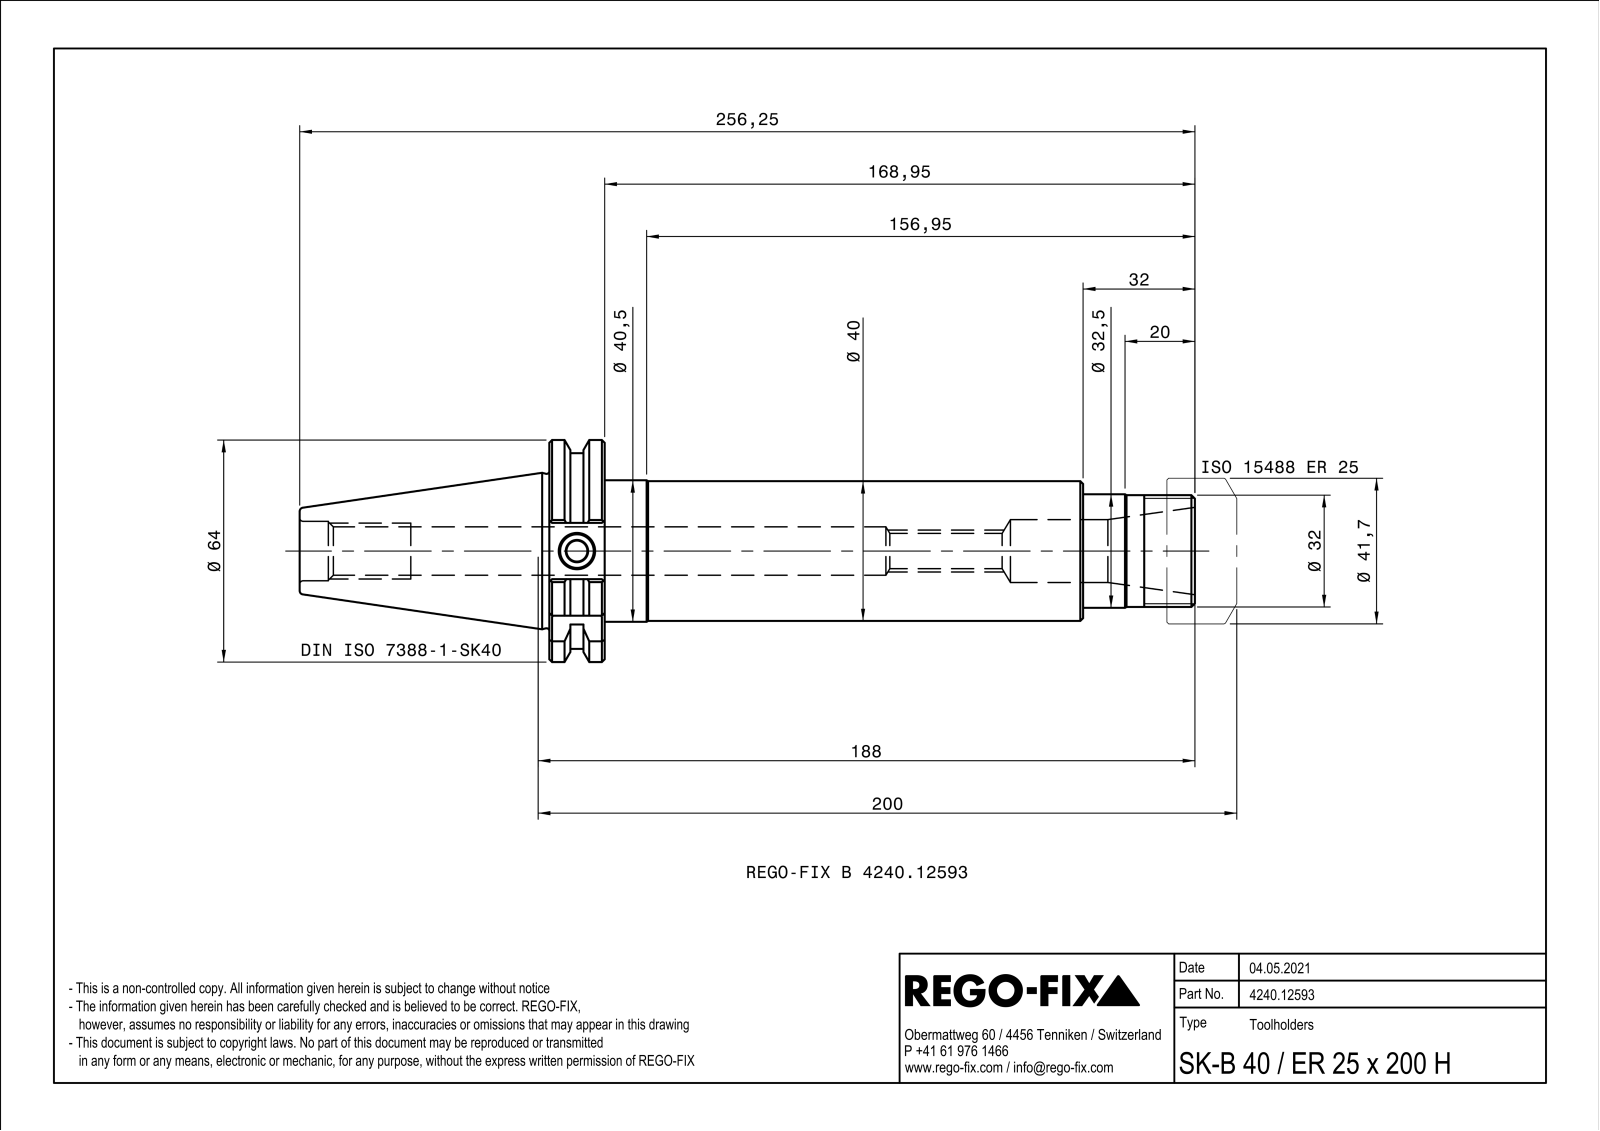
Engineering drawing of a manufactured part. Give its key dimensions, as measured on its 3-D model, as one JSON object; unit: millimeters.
{"part_name": "NOCUT", "step_written_by": "SIEMENS PLM Software Solid Edge ST10 (AUTOMOTIVE_DESIGN)", "units": "millimeters", "bodies": {"solids": 1, "faces": 160, "planar": 45, "cylindrical": 52, "other": 63}, "overall_size": [256.25, 63.55, 61.01], "volume_mm3": 265080, "surface_area_mm2": 49106, "round_holes": [[3.9, 2], [3.24, 1], [6, 1], [10, 1], [10.11, 1], [13.83, 1], [13.84, 1], [17, 1], [18, 1]], "round_bosses_or_shafts": [[40.5, 1], [40, 1], [32.5, 1], [32, 1]], "partial_cylinders_radius": [[0.5, 13], [2.25, 2], [28, 1], [31.77, 1]], "face_to_face_distances": [15.85, 168.95, 184.8, 32, 136.95, 152.8, 47.3, 16.1, 256.25, 224.25]}
